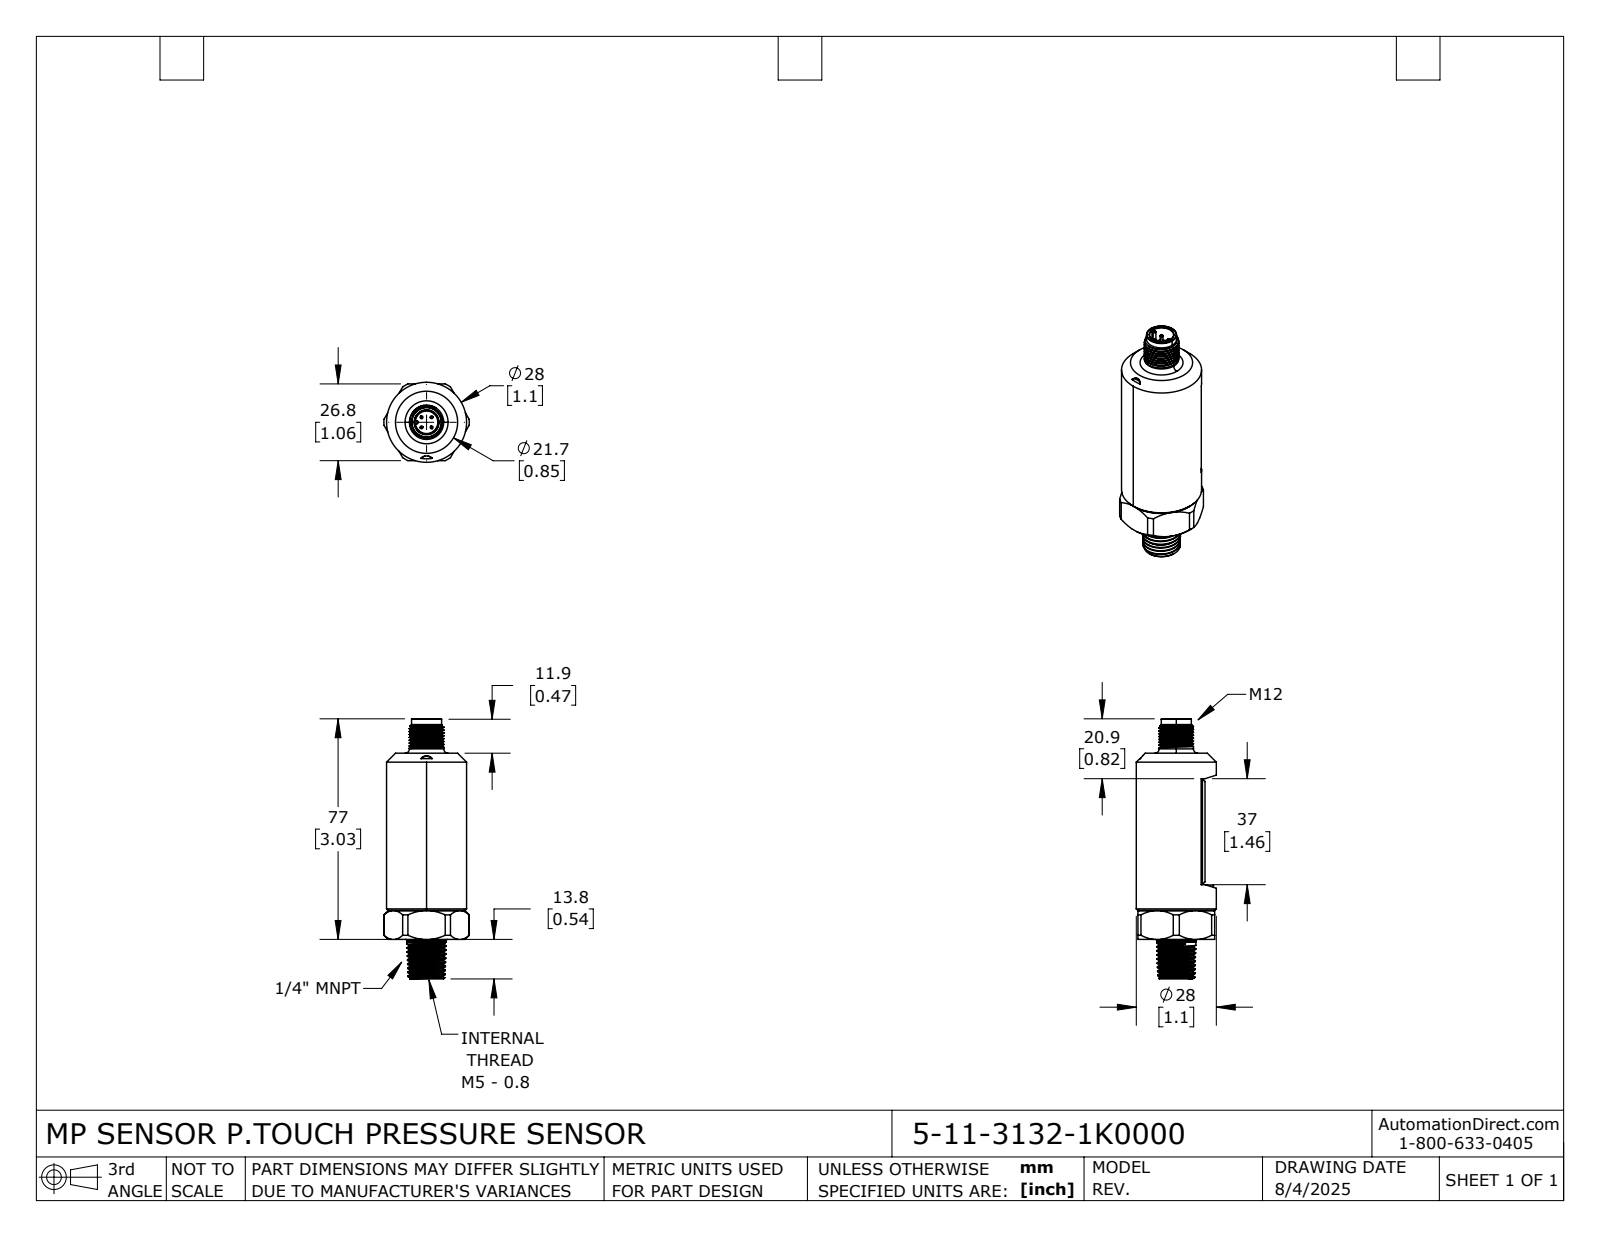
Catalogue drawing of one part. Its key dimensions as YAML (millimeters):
part_name: "5-11-3132-1K0000"
step_written_by: "SolidWorks 2024 (AUTOMOTIVE_DESIGN)"
units: millimeters
bodies: {solids: 1, faces: 199, planar: 46, cylindrical: 68, other: 85}
overall_size: [90.8, 29.8, 27.9]
volume: 39710
surface_area: 8916
round_holes:
  - {diameter: 2, count: 1}
  - {diameter: 4.2, count: 1}
  - {diameter: 8.4, count: 1}
round_bosses_or_shafts:
  - {diameter: 1, count: 4}
  - {diameter: 27.9, count: 1}
  - {diameter: 26, count: 1}
  - {diameter: 13.7, count: 1}
  - {diameter: 12, count: 1}
  - {diameter: 10.5, count: 1}
partial_cylinders:
  - {radius: 0.2, count: 2}
  - {radius: 2.3, count: 1}
  - {radius: 14.9, count: 1}
face_to_face_distances: [26.8, 65, 23.4, 3.4, 13.8, 78.8, 9, 46, 8.9, 4.7]
